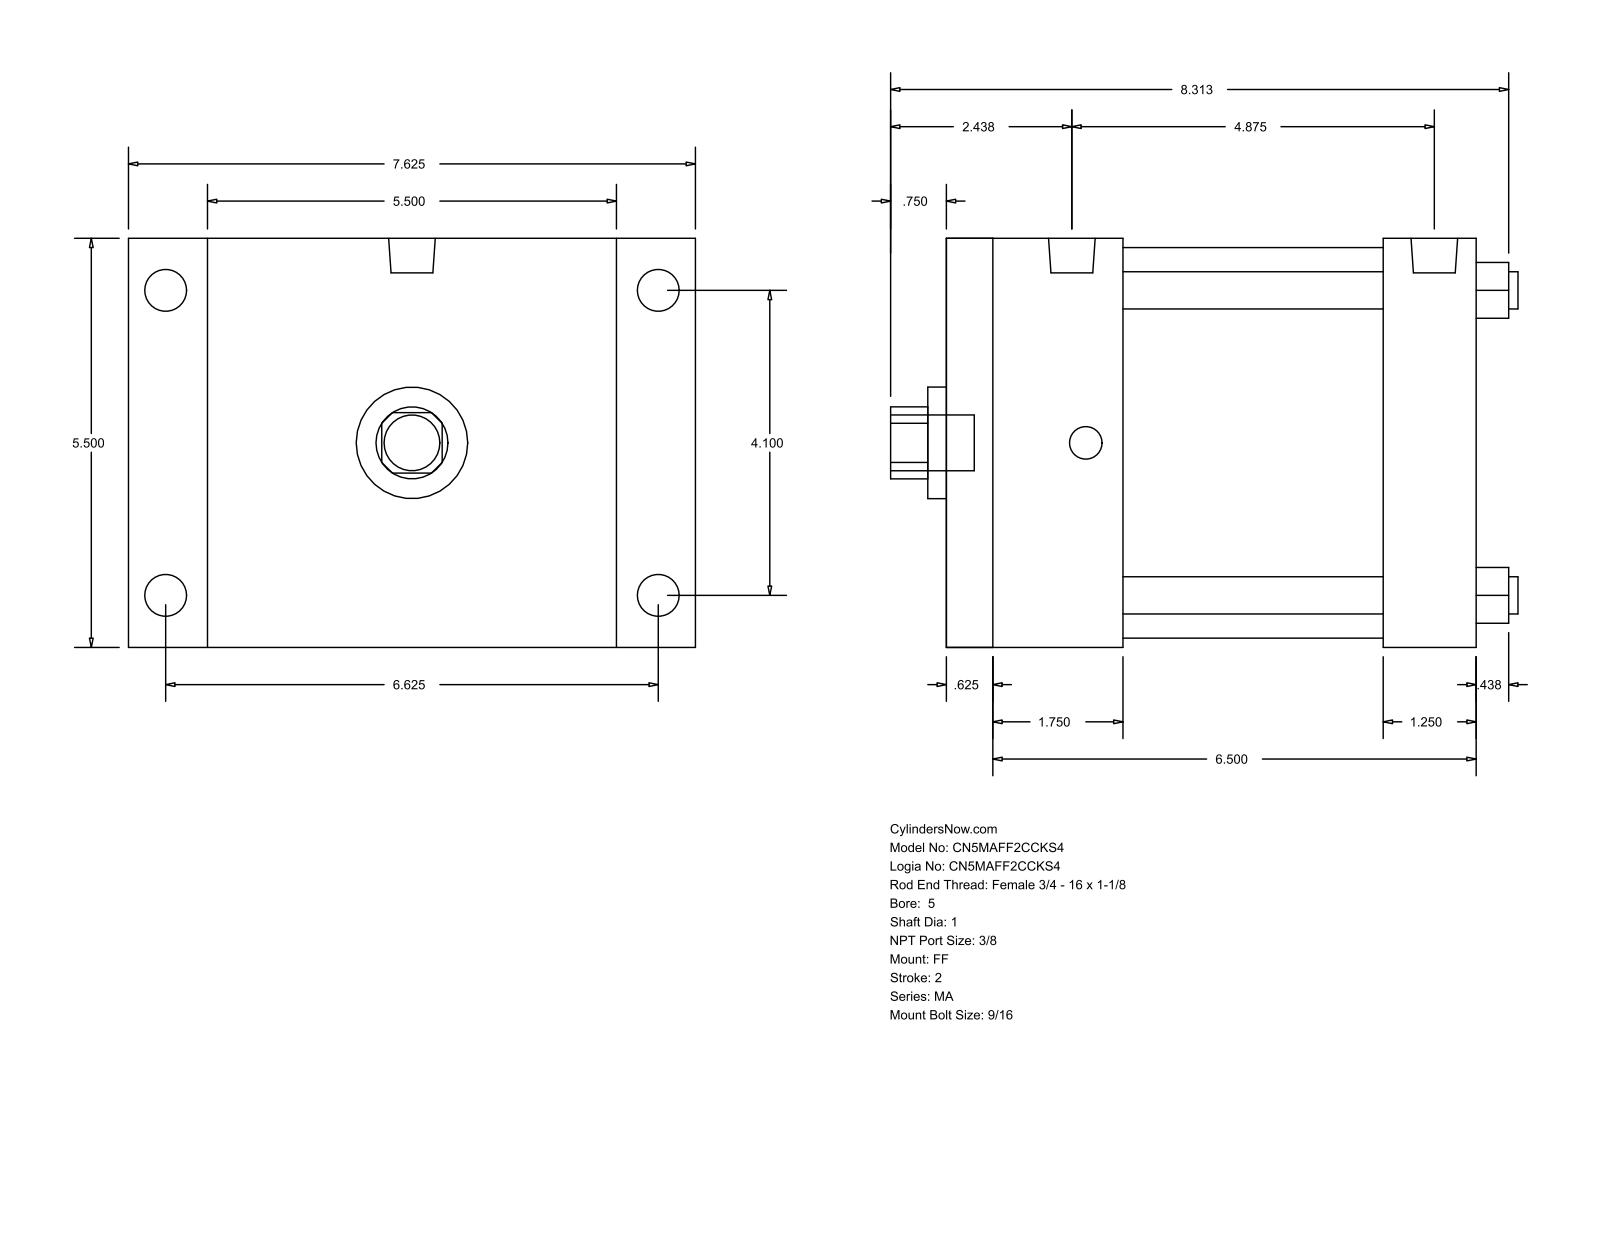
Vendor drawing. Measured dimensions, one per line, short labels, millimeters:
name: MA_FF__0500_1
written by: GSSL Pune (CONFIG_CONTROL_DESIGN)
unit: mm
bodies: 0 solids, 92 faces (64 planar, 28 cylindrical, 0 other)
size: 214.31 × 193.68 × 139.7
holes: 4× ⌀12.7, 1× ⌀25.4, 1× ⌀38.1, 1× ⌀133.35
bosses: 4× ⌀14.29, 4× ⌀11.11, 2× ⌀15.93, 1× ⌀19.05
rounds: 1× R12.29
face distances: 139.7, 180.98, 15.87, 165.11, 149.23, 133.36, 31.75, 60.33, 44.46, 88.9
hole spacings: 73.64, 104.14, 147.28
